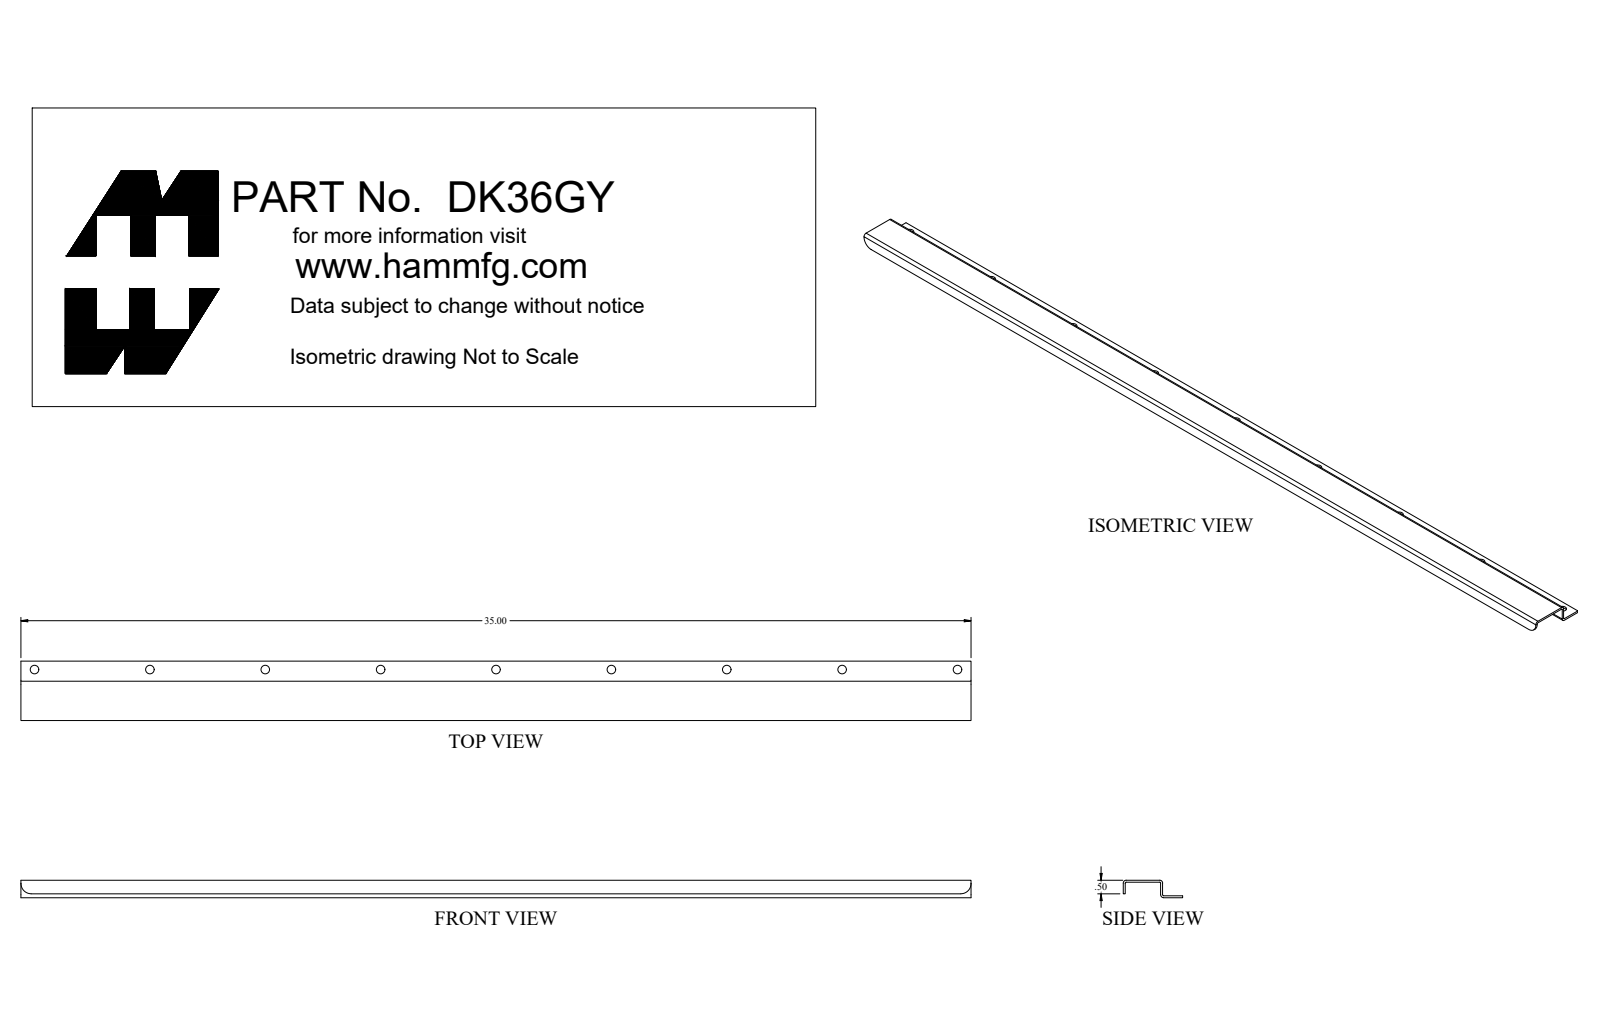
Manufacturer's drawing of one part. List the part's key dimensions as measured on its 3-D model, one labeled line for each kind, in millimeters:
Part name (STEP PRODUCT): DK36GY_Default
STEP written by: SolidWorks 2018 (CONFIG_CONTROL_DESIGN)
Units: millimetres
Bodies: 5 solids, 77 faces (35 planar, 36 cylindrical, 6 other)
Overall size (bounding box): 889 × 55.6 × 33.6
Volume: 155 900 mm³ · Surface area: 181 200 mm²
Round holes (diameter × count): ⌀8 ×9, ⌀5.1 ×1, ⌀7 ×1
Round bosses / shafts (diameter × count): ⌀15.9 ×1, ⌀12.3 ×1, ⌀6.4 ×1
Partial cylindrical surfaces — rounded edges, fillets, slot ends (radius × count): R0.9 ×3, R2.7 ×3, R9.5 ×2
Main face-to-face distances: 1.8, 14.5, 16.4, 35, 12.7, 1.6, 16.1, 18, 3.4, 36.8
Hole centre spacings: 108, 215.9, 323.9, 431.8, 539.8, 647.7, 755.7, 863.6
